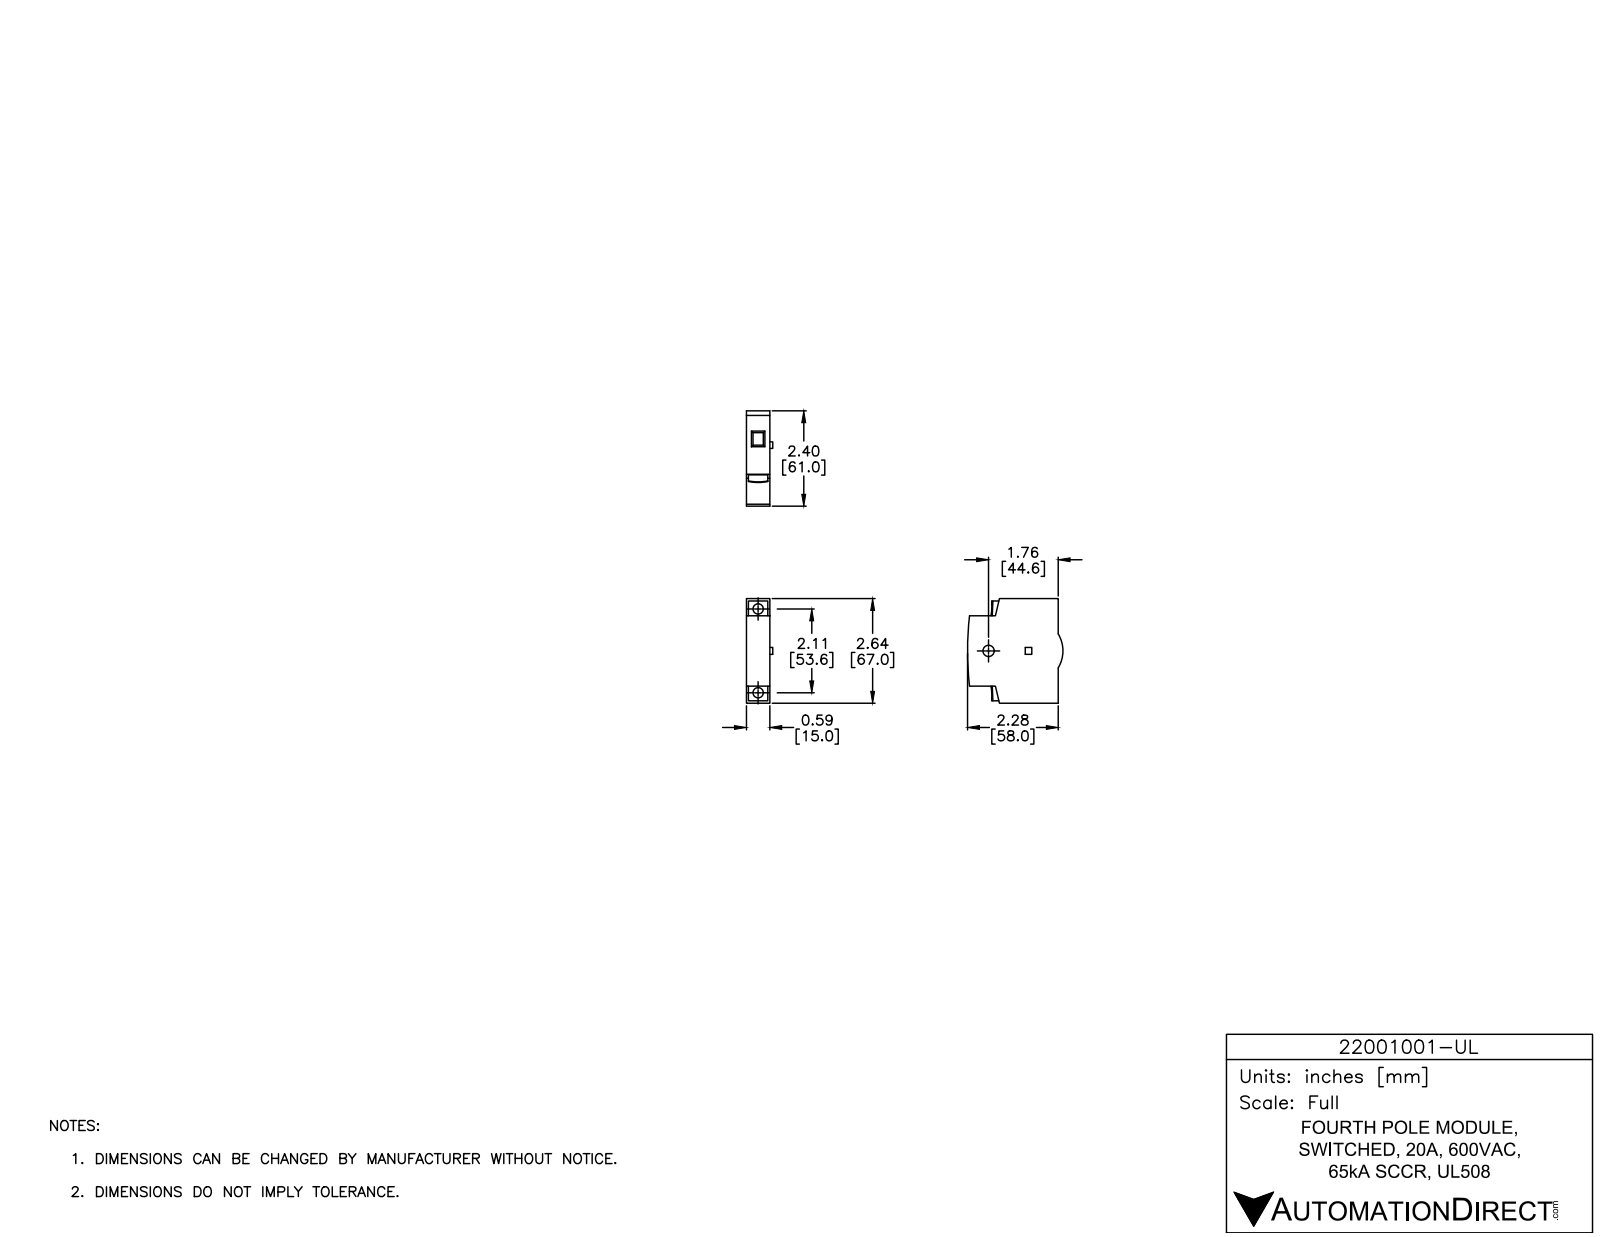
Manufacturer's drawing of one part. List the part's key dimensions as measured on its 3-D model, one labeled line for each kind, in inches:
Part name (STEP PRODUCT): 22001001-UL
STEP written by: SolidWorks 2015 (AUTOMOTIVE_DESIGN)
Units: inches
Bodies: 1 solid, 61 faces (46 planar, 11 cylindrical, 4 other)
Overall size (bounding box): 2.638 × 2.402 × 0.665
Volume: 3.141 in³ · Surface area: 18.13 in²
Round holes (diameter × count): ⌀0.26 ×2, ⌀0.283 ×1
Partial cylindrical surfaces — rounded edges, fillets, slot ends (radius × count): R0.827 ×1, R7.874 ×1
Main face-to-face distances: 0.591, 2.638, 0.433, 2.205, 1.772, 0.063, 2.575, 0.37, 2.142, 0.051
Hole centre spacings: 2.11
